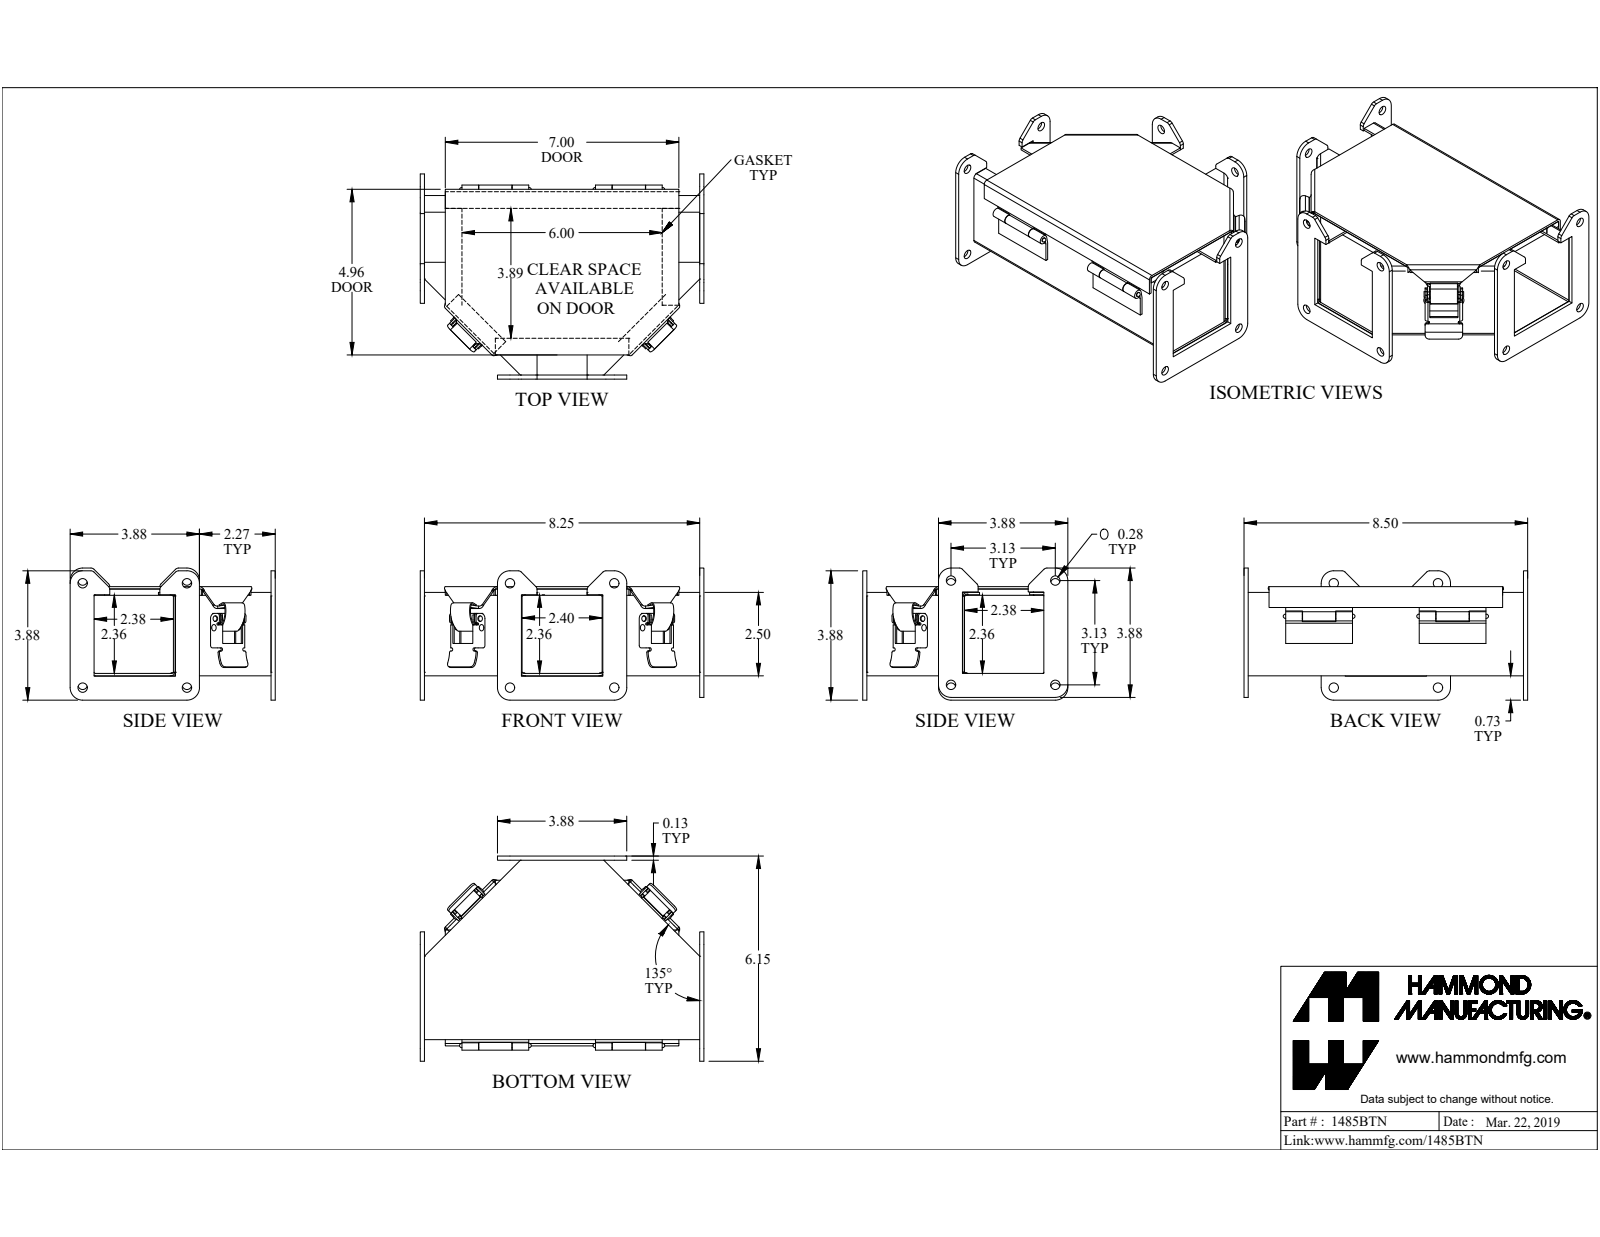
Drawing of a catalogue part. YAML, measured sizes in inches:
part_name: "1485BTN"
step_written_by: "SolidWorks 2019 (CONFIG_CONTROL_DESIGN)"
units: inches
bodies: {solids: 23, faces: 496, planar: 302, cylindrical: 158, other: 36}
overall_size: [8.5, 6.146, 3.958]
volume: 14.82
surface_area: 377.7
round_holes:
  - {diameter: 0.281, count: 12}
  - {diameter: 0.164, count: 4}
  - {diameter: 0.125, count: 1}
round_bosses_or_shafts:
  - {diameter: 0.162, count: 4}
  - {diameter: 0.158, count: 4}
  - {diameter: 0.275, count: 1}
  - {diameter: 0.275, count: 1}
  - {diameter: 0.125, count: 1}
  - {diameter: 0.125, count: 1}
partial_cylinders:
  - {radius: 0.125, count: 18}
  - {radius: 0.375, count: 12}
  - {radius: 0.036, count: 11}
  - {radius: 0.108, count: 11}
  - {radius: 0.029, count: 8}
  - {radius: 0.086, count: 8}
  - {radius: 0.078, count: 6}
  - {radius: 0.015, count: 4}
face_to_face_distances: [0.072, 2.6, 2.528, 2.672, 0.172, 2.428, 0.125, 8.375, 2.5, 0.244]
hole_center_spacings: [3.125, 4.419, 0.083, 3.126, 3.042, 3.125, 3.208, 4.361]
